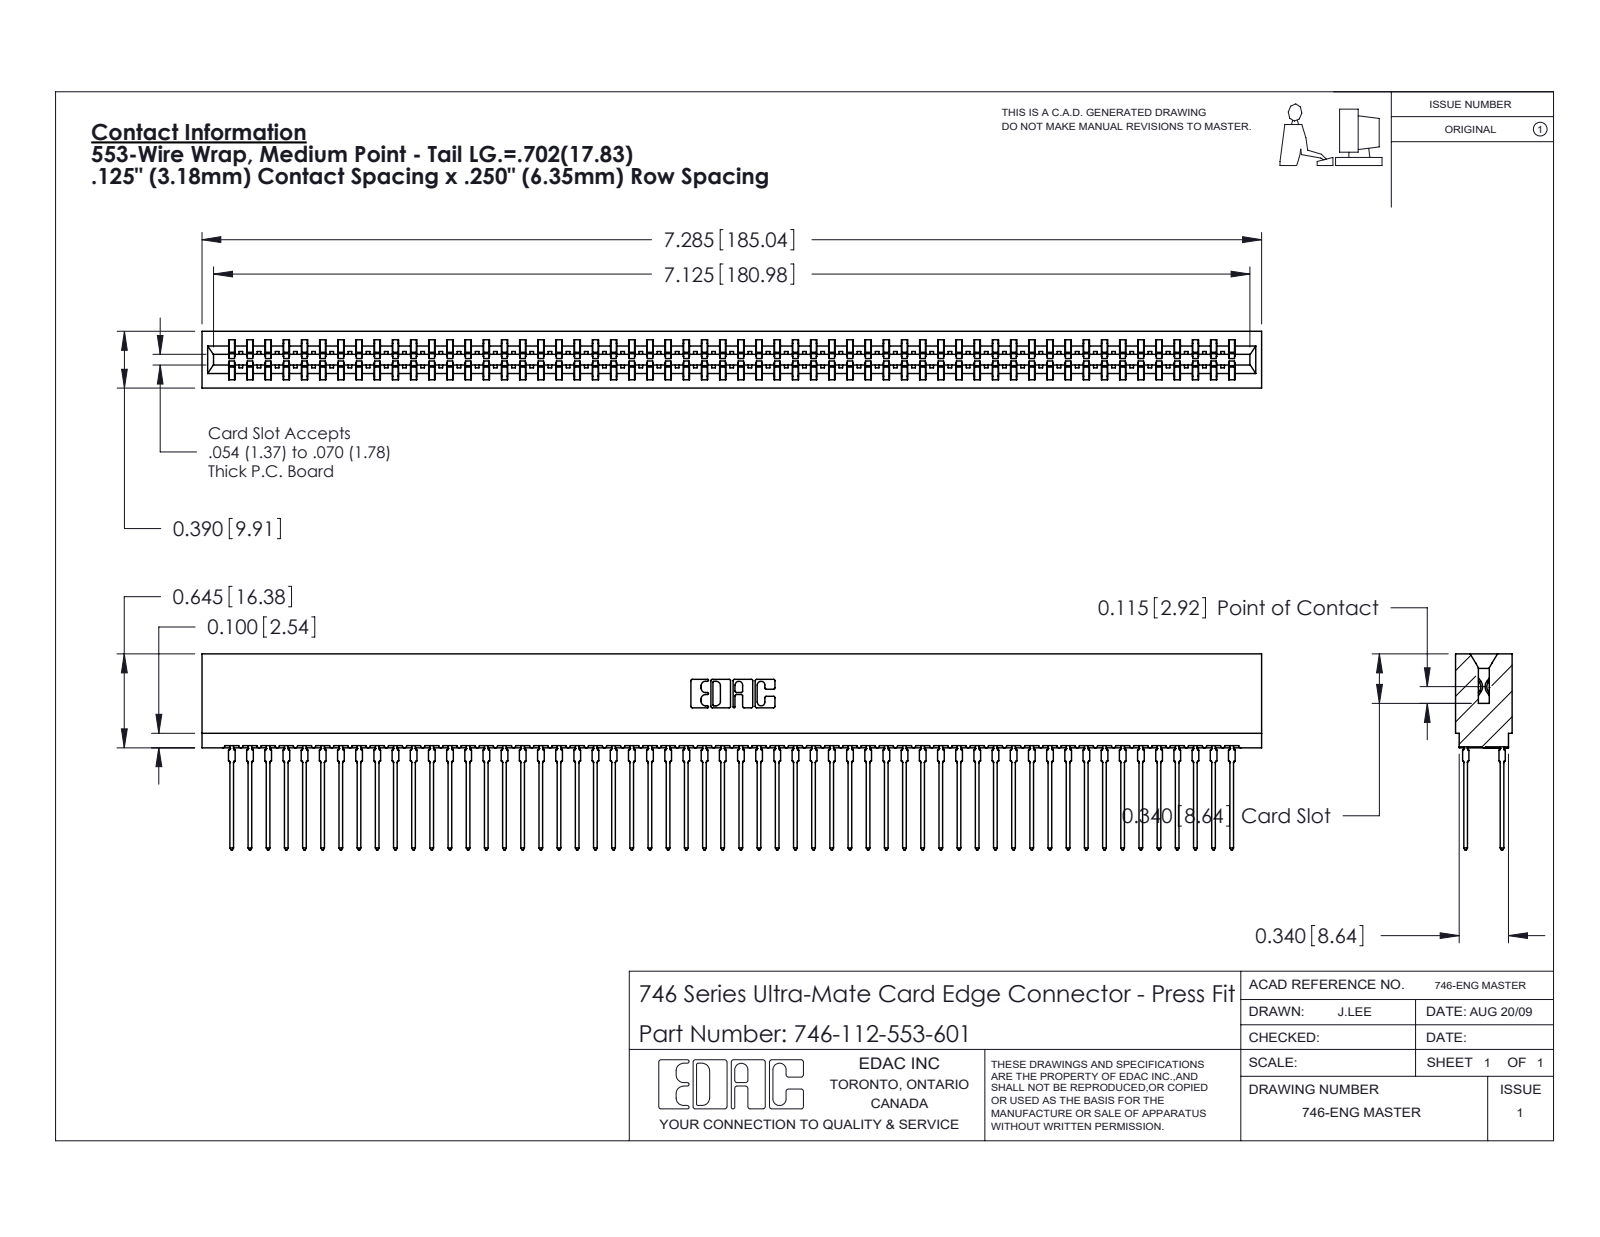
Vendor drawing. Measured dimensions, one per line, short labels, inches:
name: 746-292-001_553; 746-112-553-601; 746 Part_.340 Slot Depth - 01
written by: SolidWorks 2020 (CONFIG_CONTROL_DESIGN)
unit: in
bodies: 113 solids, 10121 faces (5207 planar, 2002 cylindrical, 2912 other)
size: 7.285 × 1.346 × 0.39
volume: 1.324 in³; area: 53.33 in²
rounds: 224× R0.021, 57× R0.015, 22× R0.01, 8× R0.005, 8× R0.011, 6× R0.007, 6× R0.031, 3× R0.026
face distances: 0.057, 0.333, 0.025, 0.25, 0.307, 0.39, 0.083, 0.275, 0.225, 0.015
